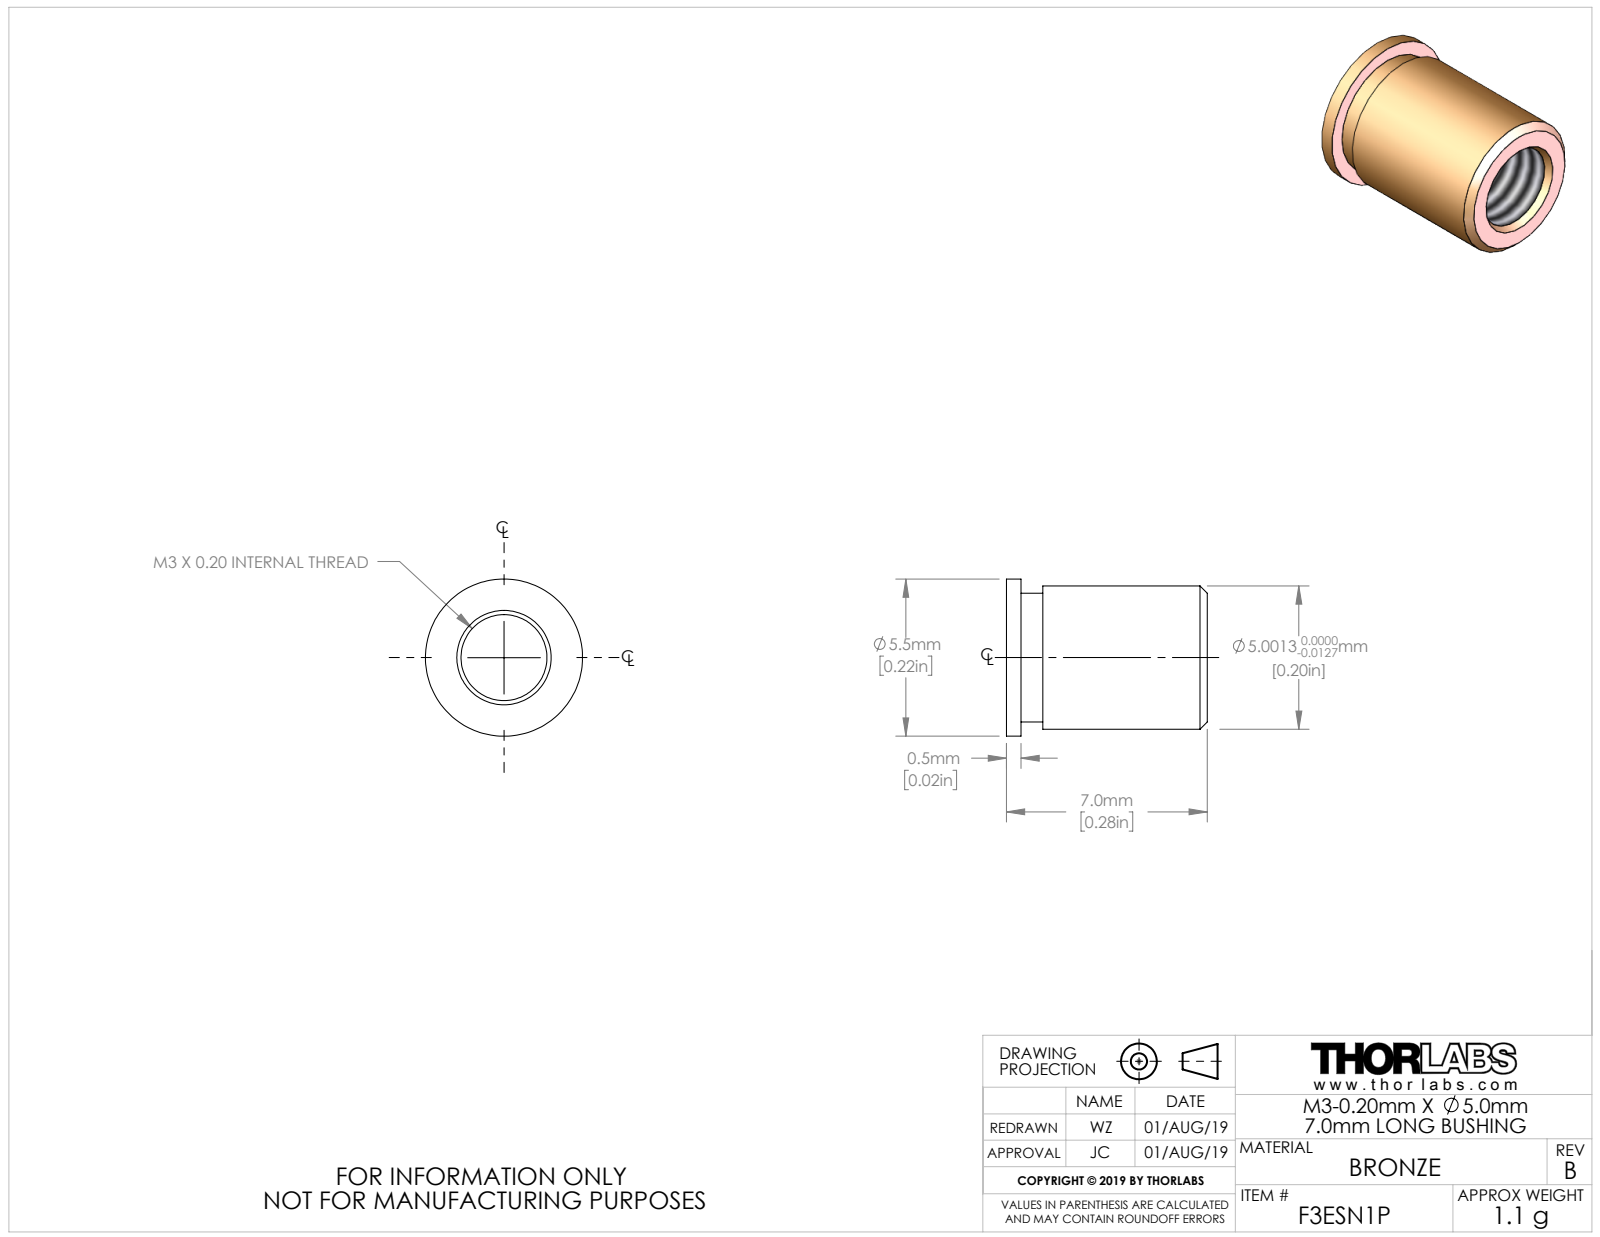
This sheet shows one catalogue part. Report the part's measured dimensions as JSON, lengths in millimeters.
{"part_name": "18996-E0W", "step_written_by": "SolidWorks 2007 (AUTOMOTIVE_DESIGN)", "units": "millimeters", "bodies": {"solids": 1, "faces": 18, "planar": 4, "cylindrical": 8, "other": 6}, "overall_size": [7.01, 5.49, 5.49], "volume_mm3": 86, "surface_area_mm2": 212, "round_holes": [[3, 1]], "round_bosses_or_shafts": [[5.49, 1], [5, 1], [4.49, 1]], "face_to_face_distances": [0.51, 7.02, 6.51, 1.27, 0.76, 5.75]}
